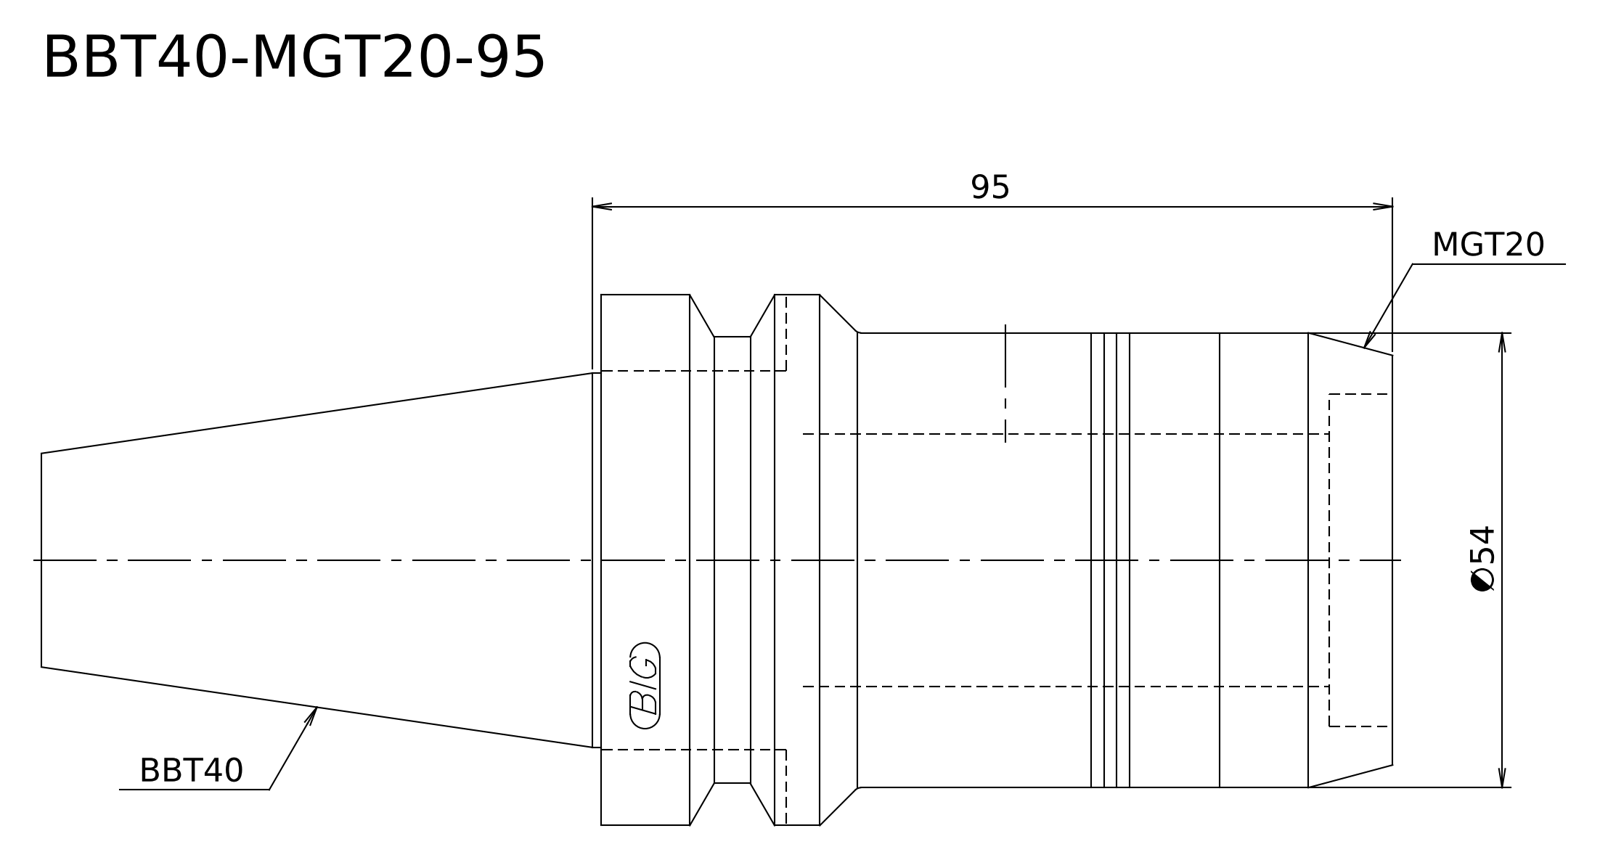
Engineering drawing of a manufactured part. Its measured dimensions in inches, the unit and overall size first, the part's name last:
Units: inches
Overall size (bounding box): 6.315 × 2.48 × 2.48
Round bosses / shafts (diameter × count): ⌀2.48 ×1, ⌀2.126 ×1, ⌀2.087 ×1, ⌀1.75 ×1
Main face-to-face distances: 3.701, 6.315, 2.614
Volume: 18.04 in³ · Surface area: 45.27 in²
Bodies: 1 solid, 13 faces (3 planar, 5 cylindrical, 5 other)
STEP written by: Kubotek KeyCreator V8.5.1 (14335) (CONFIG_CONTROL_DESIGN)
